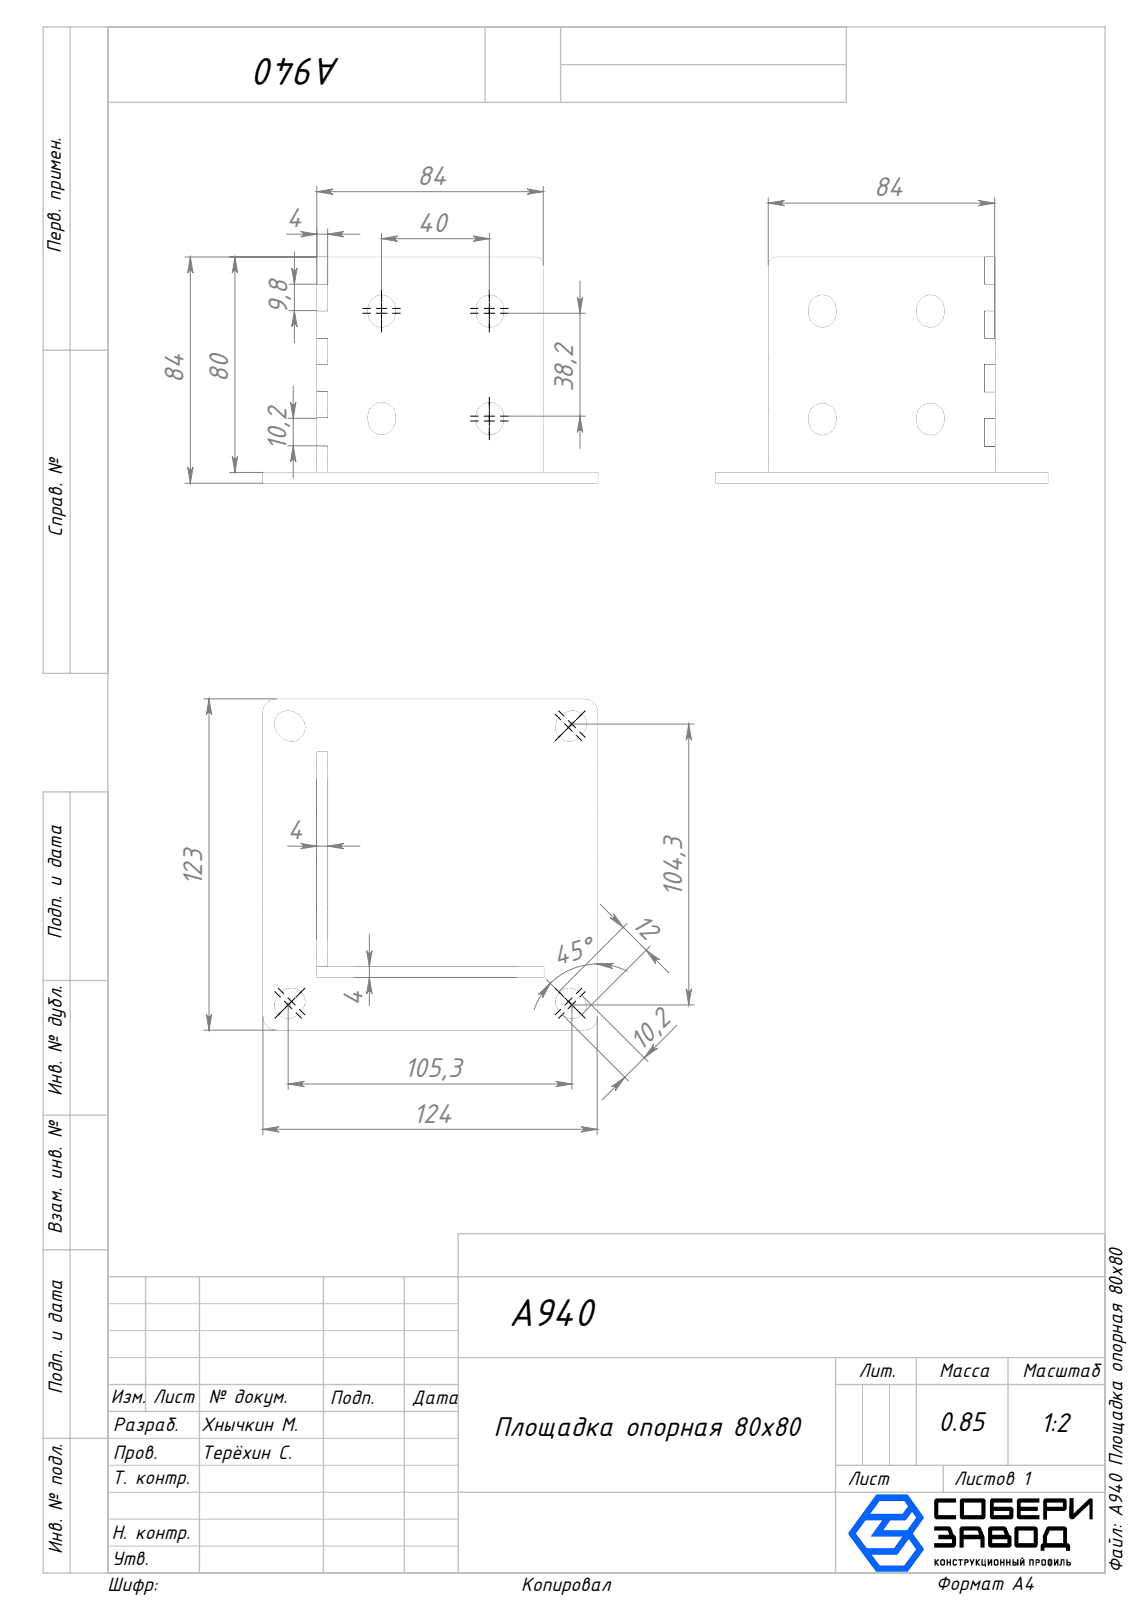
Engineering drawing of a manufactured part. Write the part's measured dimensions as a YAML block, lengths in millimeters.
part_name: "A940 Площадка опорная 80х80; A940 80x80 основание_00; A940 80x80 Боковина с пазом 1_00; A940 80x80 Боковина с пазом 2_00"
step_written_by: "SolidWorks 2025 (AUTOMOTIVE_DESIGN)"
units: millimeters
bodies: {solids: 3, faces: 124, planar: 86, cylindrical: 38, other: 0}
overall_size: [124, 123, 84]
volume: 108453
surface_area: 61782
partial_cylinders:
  - {radius: 5.1, count: 24}
  - {radius: 5, count: 4}
  - {radius: 3, count: 2}
face_to_face_distances: [4, 84, 80, 4.1, 20, 19.5, 103.5, 104, 79.9, 4.2]
